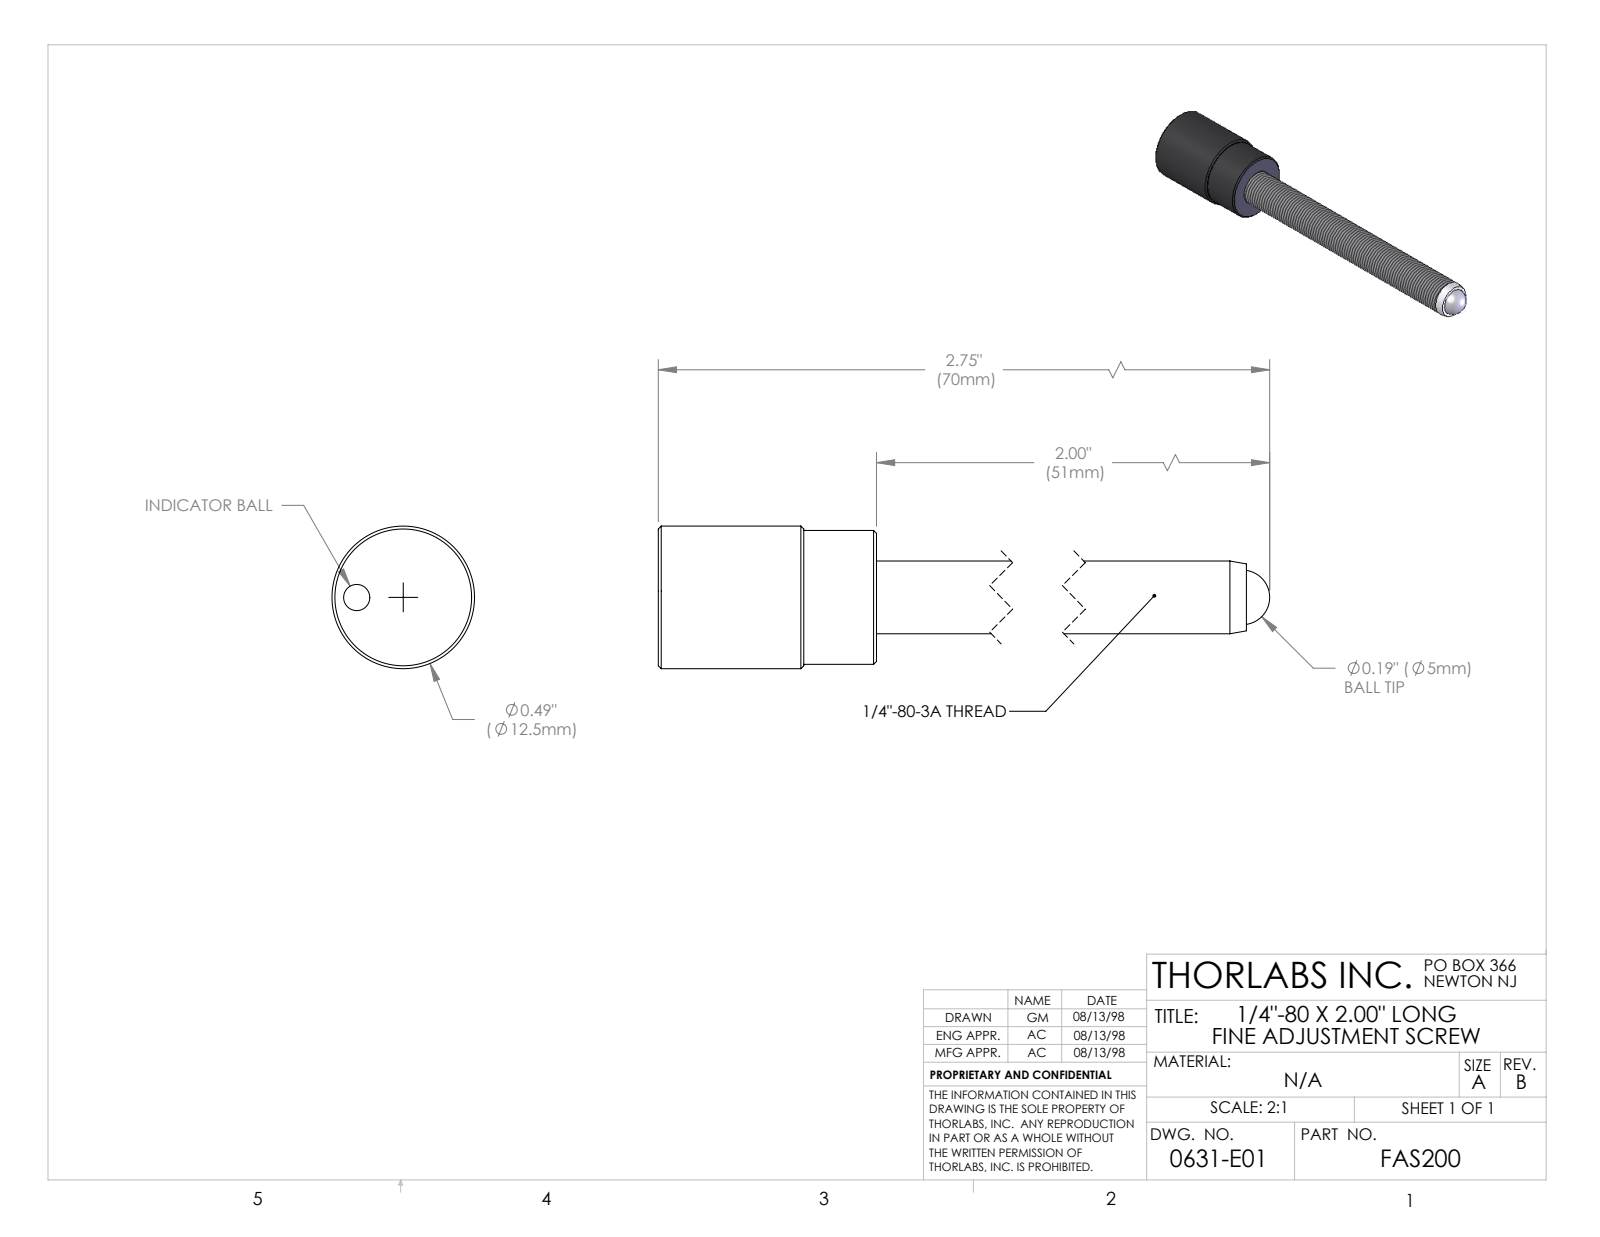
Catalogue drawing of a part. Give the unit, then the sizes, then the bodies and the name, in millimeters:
Units: millimetres
Overall size (bounding box): 69.85 × 12.45 × 12.45
Round holes (diameter × count): ⌀2.29 ×1, ⌀4.78 ×1, ⌀5.94 ×1, ⌀6.3 ×1
Round bosses / shafts (diameter × count): ⌀12.45 ×1, ⌀11.68 ×1, ⌀6.35 ×1
Main face-to-face distances: 19.05, 6.35, 12.7, 67.82, 61.47, 48.77, 55.12, 2.29, 4.06, 10.41
Hole centre spacings: 4.07
Volume: 3 808 mm³ · Surface area: 2 613 mm²
Bodies: 4 solids, 40 faces (8 planar, 14 cylindrical, 18 other)
Part name (STEP PRODUCT): 0631-E0W
STEP written by: SolidWorks 2007 (AUTOMOTIVE_DESIGN)
